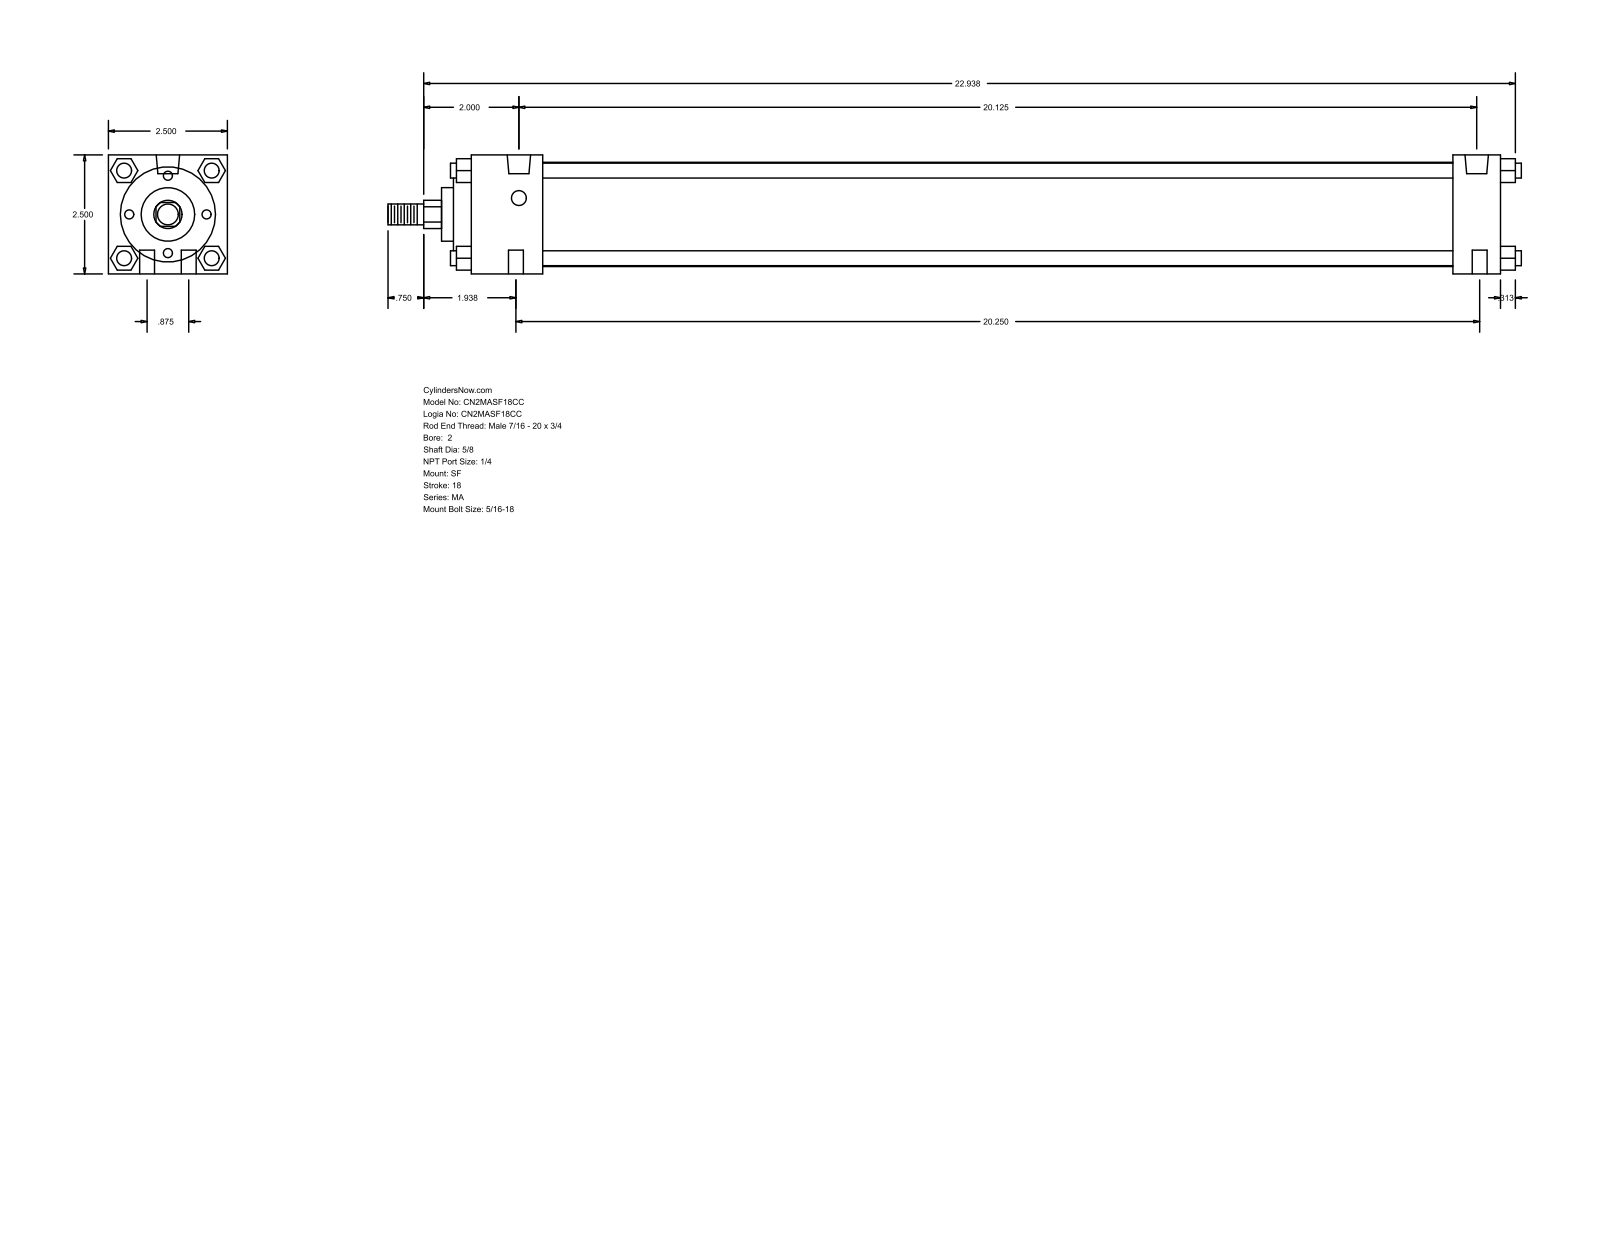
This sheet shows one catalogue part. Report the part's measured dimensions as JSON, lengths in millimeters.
{"part_name": "MA_SF__0200_0.625", "step_written_by": "GSSL Pune (CONFIG_CONTROL_DESIGN)", "units": "millimeters", "bodies": {"solids": 0, "faces": 126, "planar": 95, "cylindrical": 31, "other": 0}, "overall_size": [604.84, 63.5, 63.5], "round_holes": [[7.94, 6], [12.49, 2]], "round_bosses_or_shafts": [[7.94, 4], [55.63, 1], [50.8, 1], [28.57, 1], [15.88, 1], [11.11, 1]], "partial_cylinders_radius": [[7.54, 1]], "face_to_face_distances": [63.5, 25.4, 12.7, 38.1, 549.27, 523.87, 485.77, 511.17, 9.52, 47.62], "hole_center_spacings": [11.22, 22.22, 511.18, 512.88, 512.89, 514.35, 514.83]}
